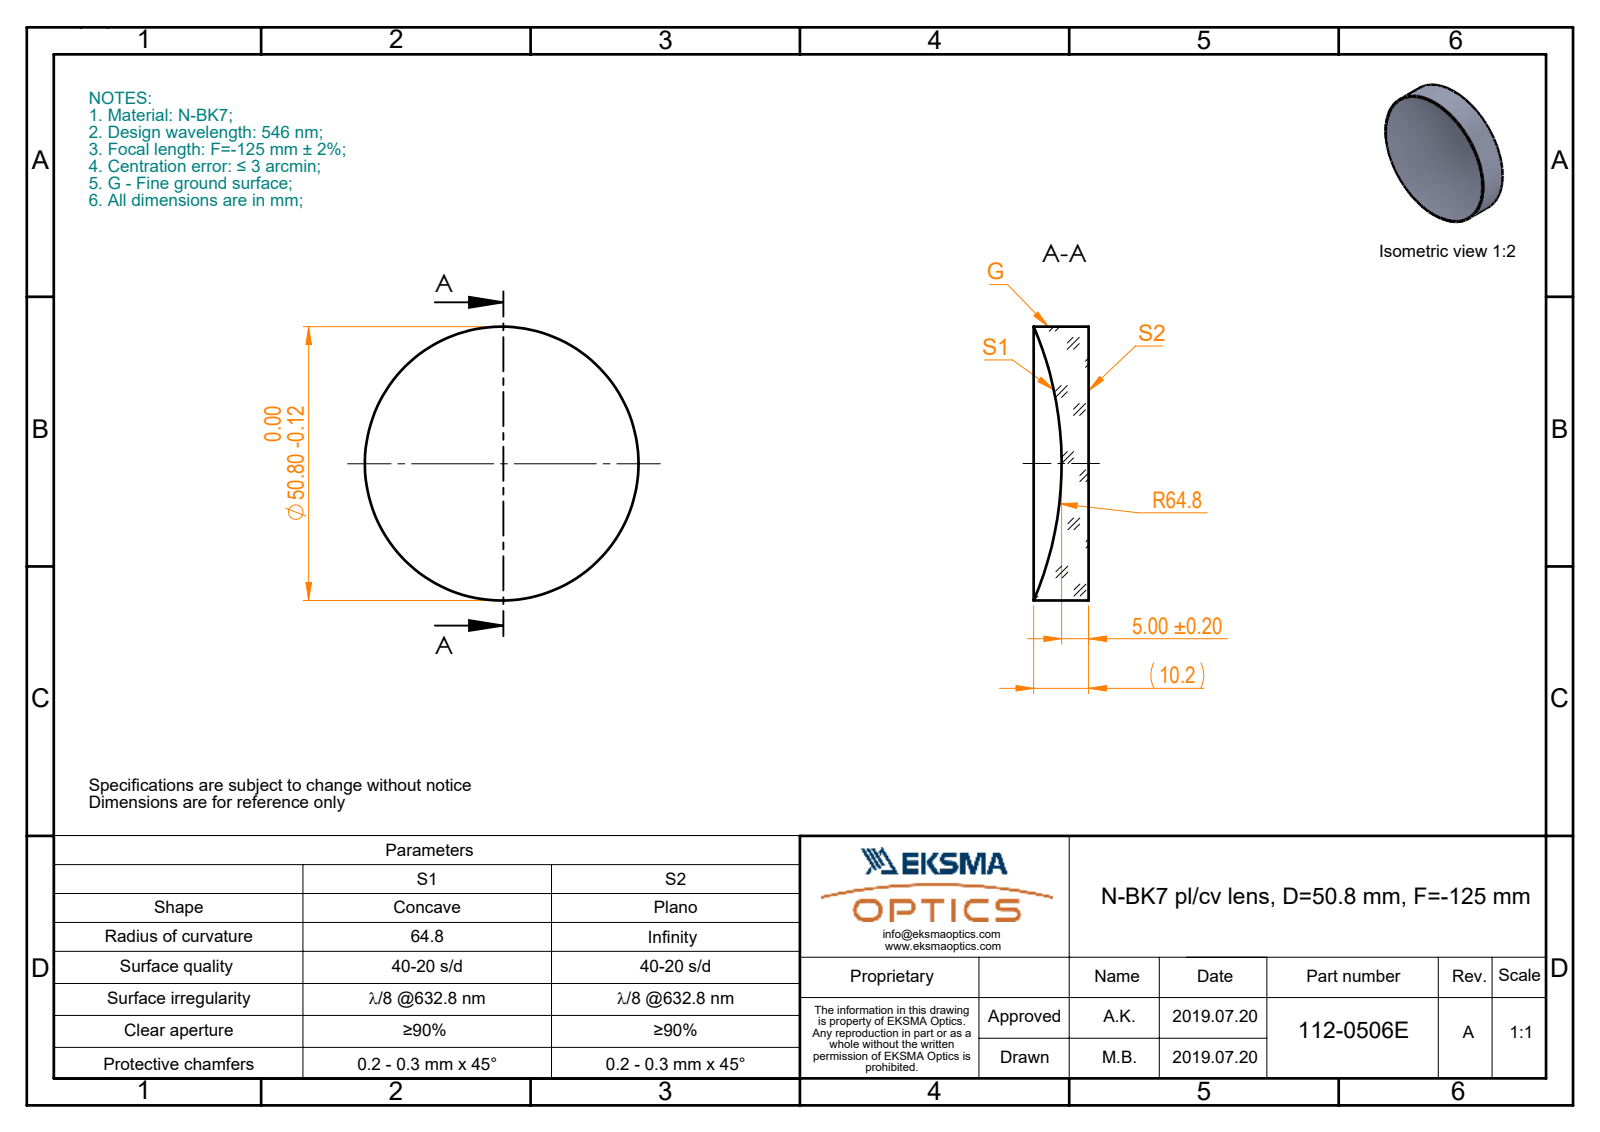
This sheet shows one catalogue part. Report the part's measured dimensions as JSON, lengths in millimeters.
{"part_name": "112-0506 BK7 pl-cv 50.8 F-125", "step_written_by": "SolidWorks 2017 (CONFIG_CONTROL_DESIGN)", "units": "millimeters", "bodies": {"solids": 1, "faces": 5, "planar": 1, "cylindrical": 2, "other": 2}, "overall_size": [50.8, 50.8, 10.18], "volume_mm3": 15313, "surface_area_mm2": 5763, "round_bosses_or_shafts": [[50.8, 1]]}
